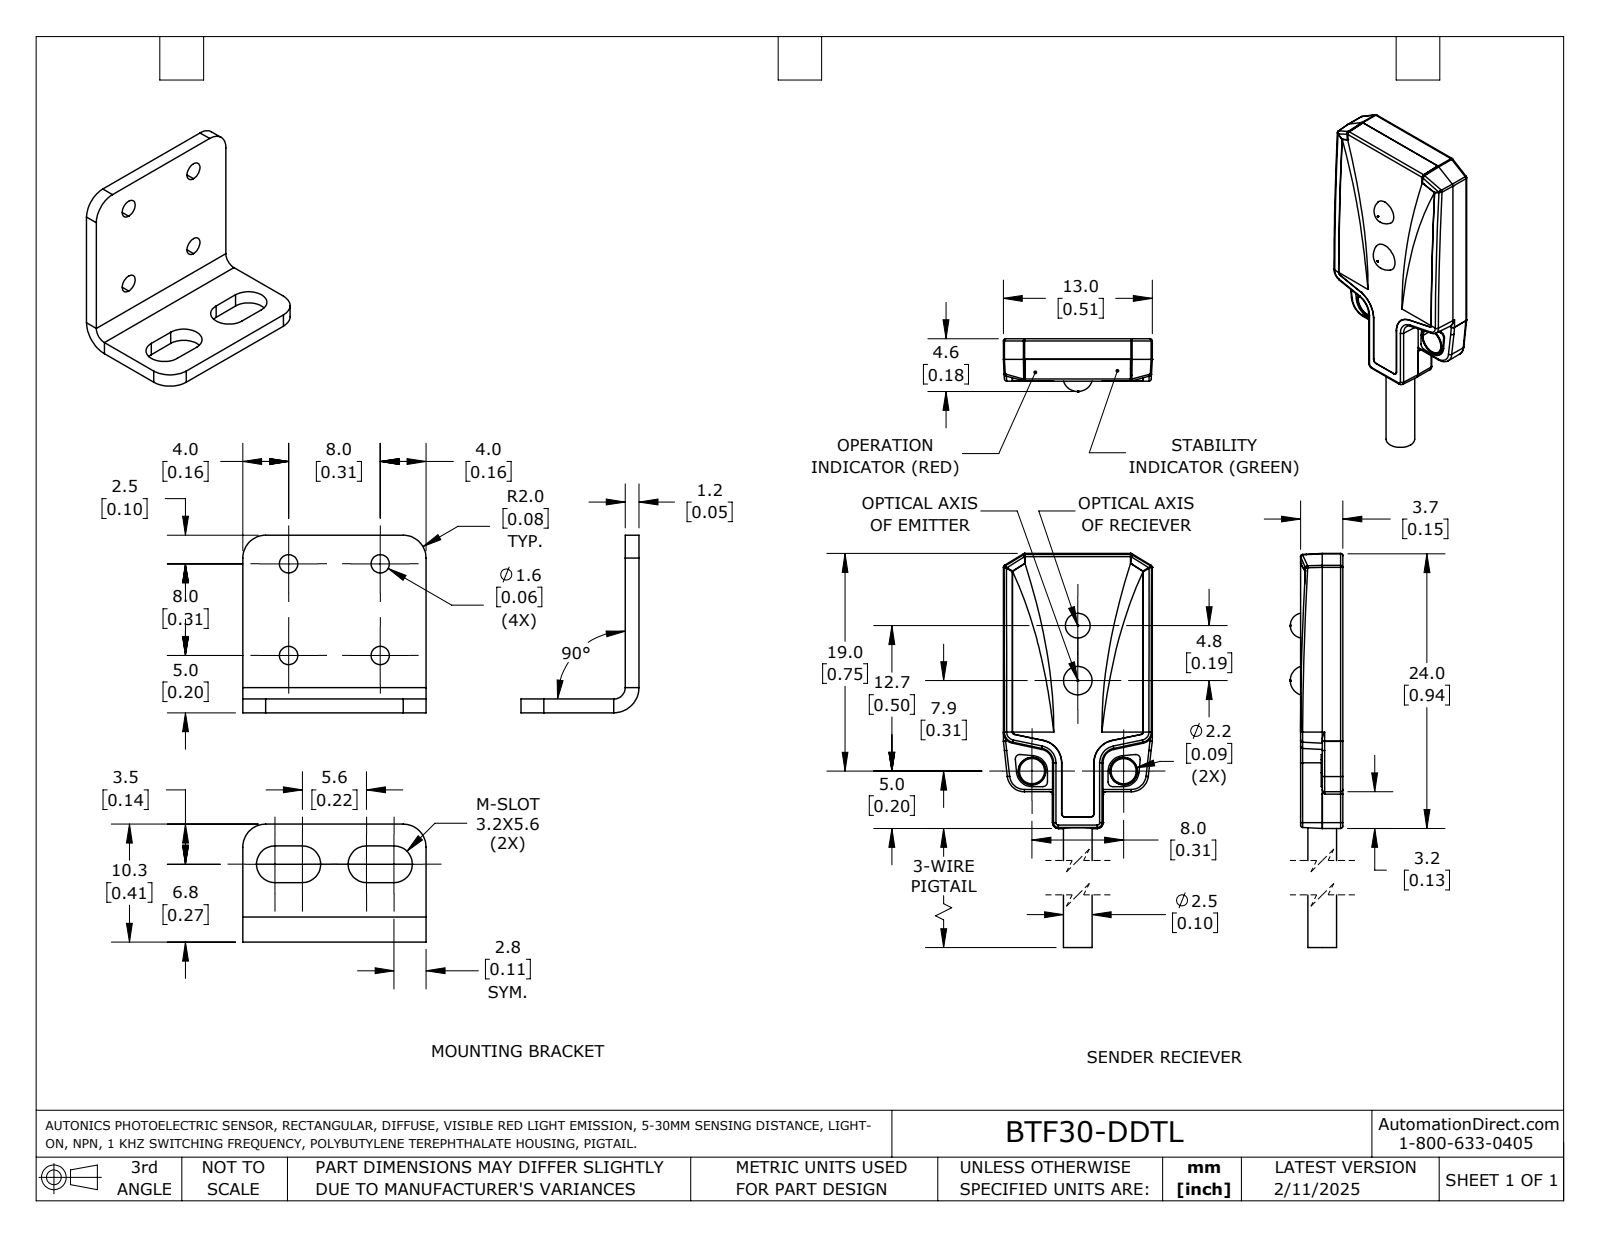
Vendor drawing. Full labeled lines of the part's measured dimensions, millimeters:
Part name (STEP PRODUCT): BTF30-DDTL_BTF30-DDTL-P_BTF30-DDTD_BTF30-DDTD-P
STEP written by: SolidWorks 2024 (AUTOMOTIVE_DESIGN)
Units: millimetres
Bodies: 6 solids, 413 faces (175 planar, 126 cylindrical, 112 other)
Overall size (bounding box): 31.5 × 15.5 × 14.9
Volume: 1 446 mm³ · Surface area: 1 936 mm²
Round holes (diameter × count): ⌀1.6 ×4, ⌀2.2 ×2, ⌀2.4 ×2
Round bosses / shafts (diameter × count): ⌀3.6 ×2, ⌀3.5 ×2, ⌀2.36 ×2, ⌀2 ×2, ⌀2.5 ×1
Partial cylindrical surfaces — rounded edges, fillets, slot ends (radius × count): R0.2 ×41, R2 ×6, R0.4 ×4, R1.6 ×4, R1 ×3, R0.22 ×2, R0.3 ×2, R0.32 ×2
Main face-to-face distances: 1.2, 3.7, 4.9, 2.5, 1.9, 14.3, 15.5, 1.8, 1.3, 12.2
Hole centre spacings: 8, 11.31
